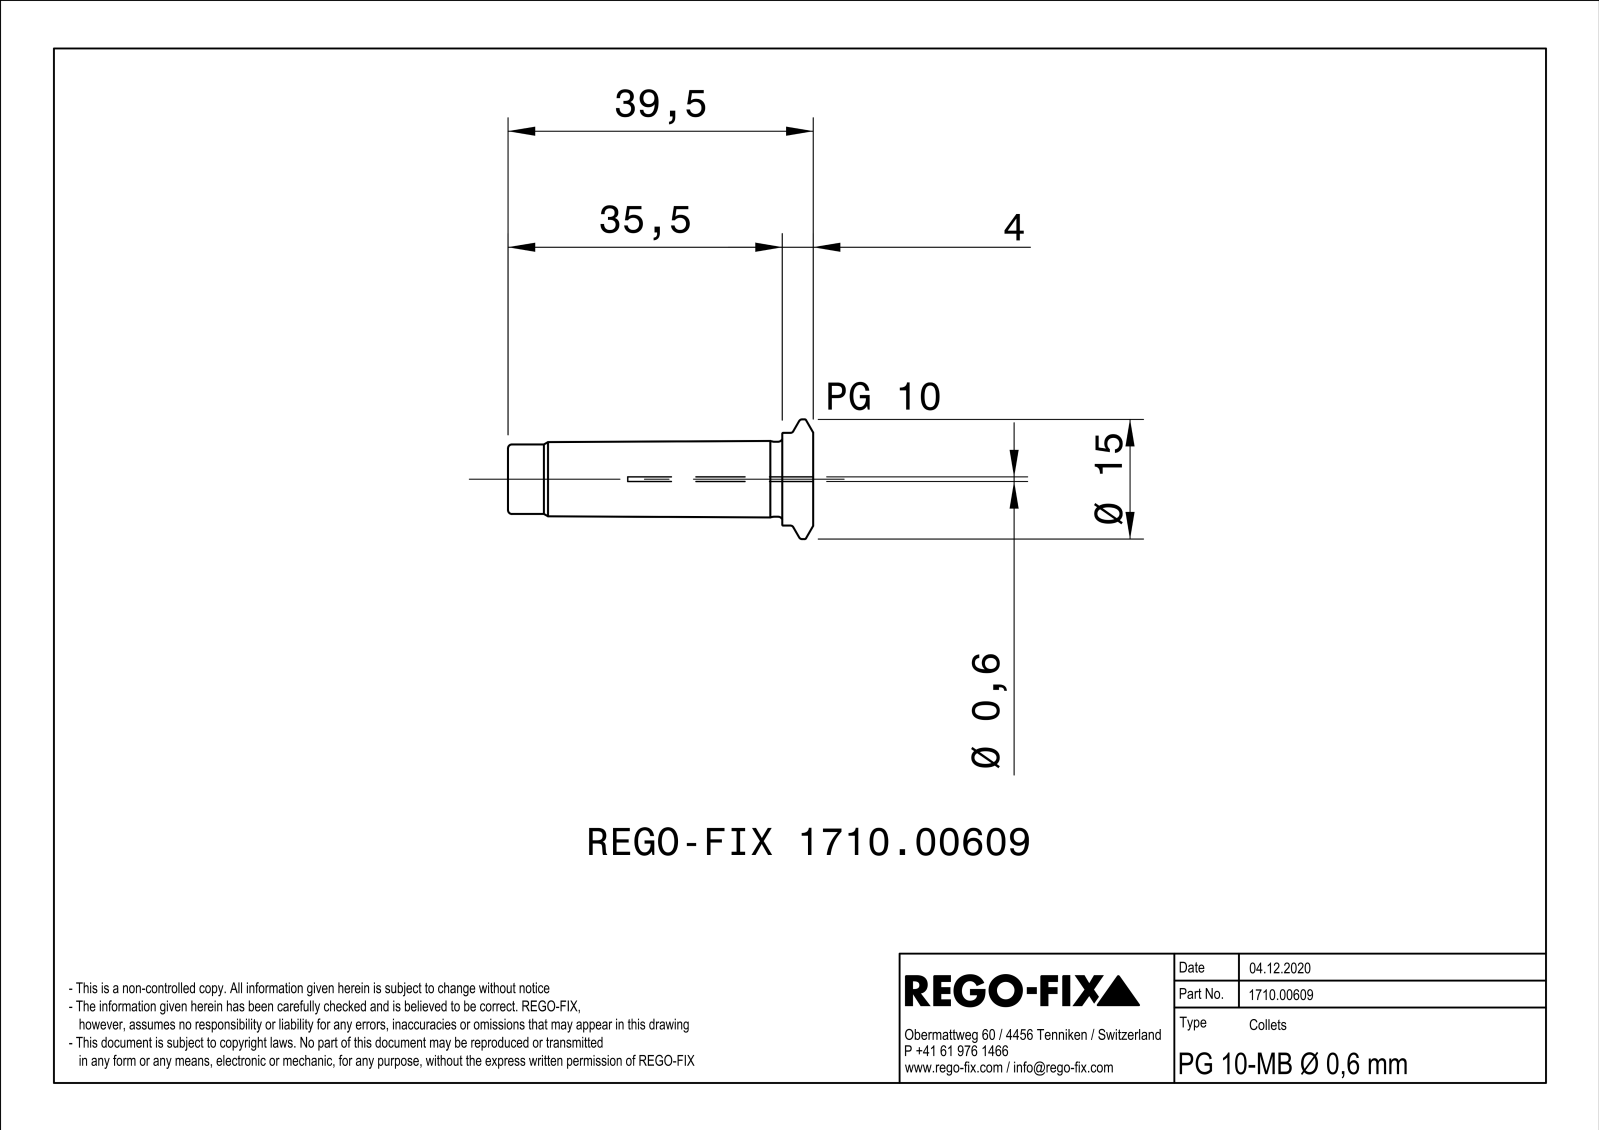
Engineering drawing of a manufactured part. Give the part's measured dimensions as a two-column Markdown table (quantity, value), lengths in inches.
| quantity | value |
| --- | --- |
| part name | NOCUT |
| STEP written by | SIEMENS PLM Software Solid Edge ST10 (AUTOMOTIVE_DESIGN) |
| units | inches |
| bodies | 1 solid, 79 faces (21 planar, 18 cylindrical, 40 other) |
| overall size | 1.555 × 0.61 × 0.61 |
| volume | 0.139 in³ |
| surface area | 4.143 in² |
| round holes (diameter × count) | 0.079 × 3, 0.024 × 1, 0.244 × 1, 0.268 × 1 |
| round bosses / shafts (diameter × count) | 0.61 × 1, 0.472 × 1, 0.382 × 1, 0.354 × 1 |
| main face-to-face distances | 0.024, 1.555, 0.768, 0.787, 1.398, 0.63, 0.157 |
| hole center spacings | 0.079, 0.136 |
